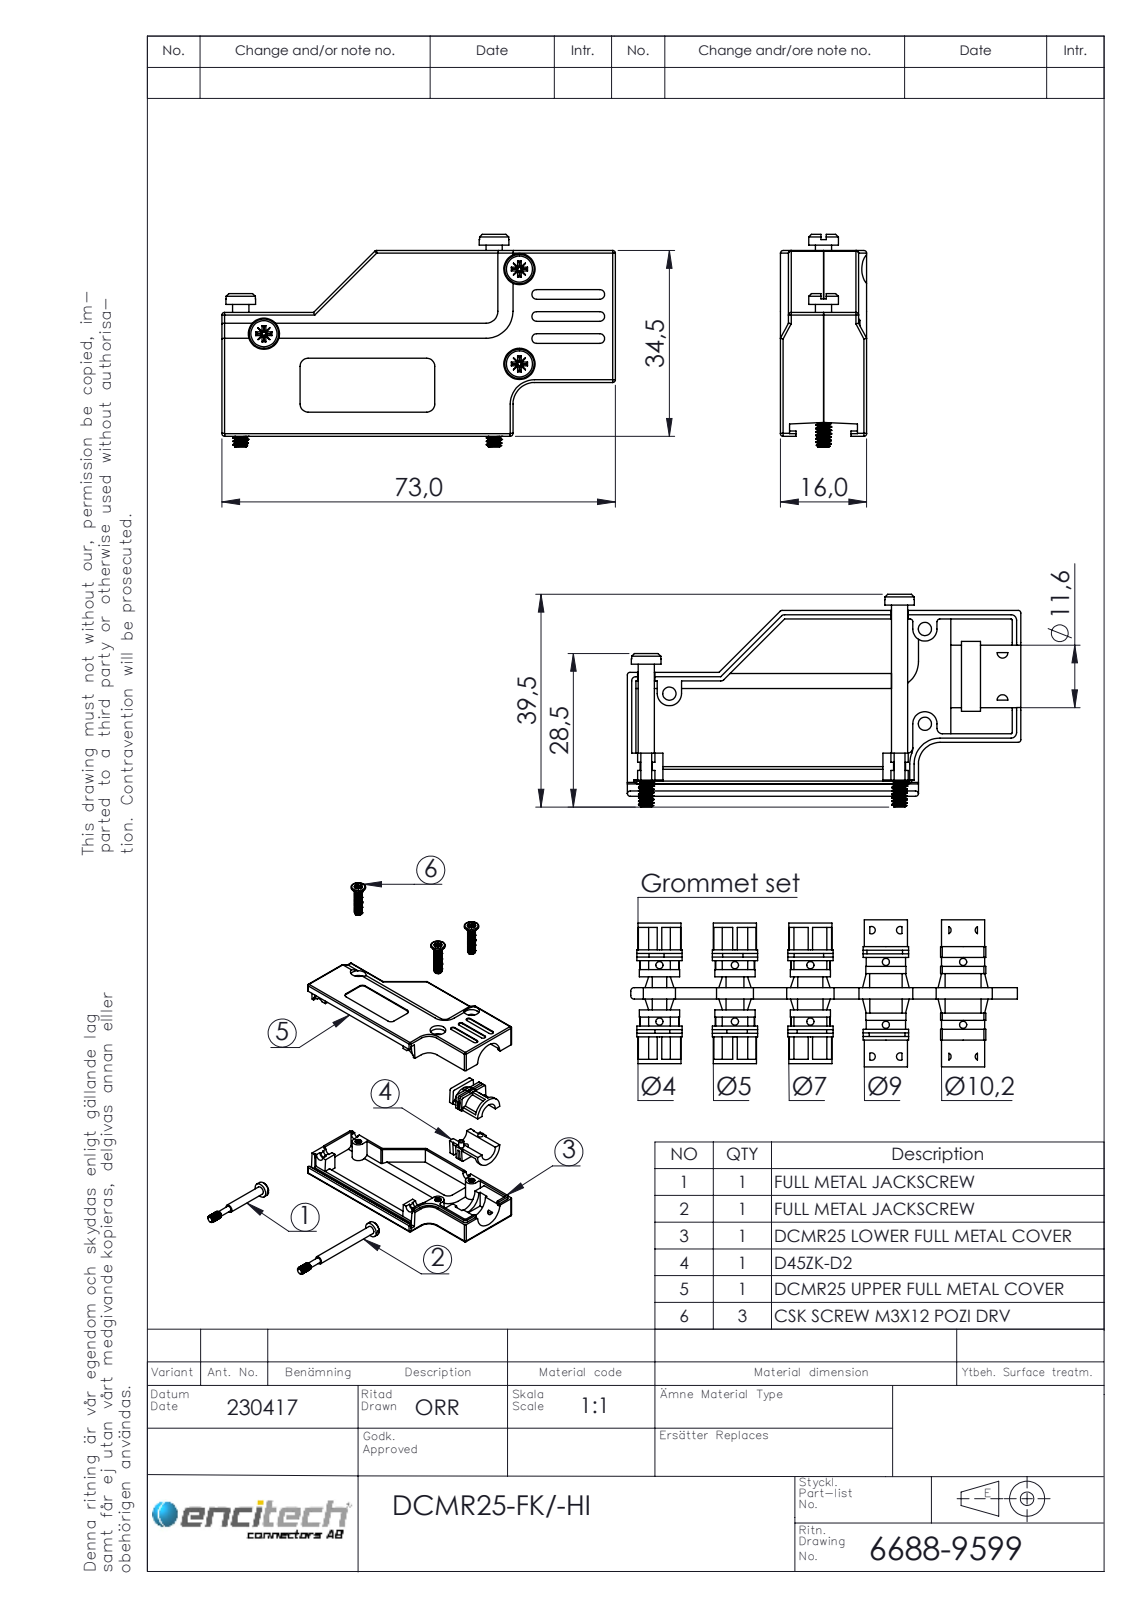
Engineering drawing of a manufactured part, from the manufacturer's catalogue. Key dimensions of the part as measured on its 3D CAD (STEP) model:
Part name (STEP PRODUCT): 6805-0501-03; 6826-0128-12; 6855-0117-02; 6522-0121-05 (7mm) (+3 more)
STEP written by: SolidWorks 2021 (AUTOMOTIVE_DESIGN)
Units: millimetres
Bodies: 9 solids, 949 faces (393 planar, 454 cylindrical, 102 other)
Overall size (bounding box): 73 × 39.5 × 16
Volume: 13 663 mm³ · Surface area: 16 735 mm²
Round holes (diameter × count): ⌀2 ×3, ⌀3.3 ×3, ⌀2.46 ×2, ⌀3.2 ×2, ⌀5.8 ×2, ⌀2.45 ×1, ⌀7 ×1, ⌀11.6 ×1
Round bosses / shafts (diameter × count): ⌀2.9 ×3, ⌀5.5 ×2, ⌀3 ×2, ⌀2.84 ×2, ⌀2 ×2, ⌀1.9 ×2, ⌀9.2 ×1
Partial cylindrical surfaces — rounded edges, fillets, slot ends (radius × count): R0.5 ×44, R0.1 ×12, R2.25 ×7, R0.9 ×6, R1 ×6, R0.55 ×4, R0.8 ×4, R1.5 ×4
Main face-to-face distances: 14.2, 1.8, 1.5, 12.4, 12.7, 8, 16, 6.2, 1.6, 1.2
Hole centre spacings: 5.71, 9.27, 10.48, 16.18, 10, 17.6, 47, 47.73
